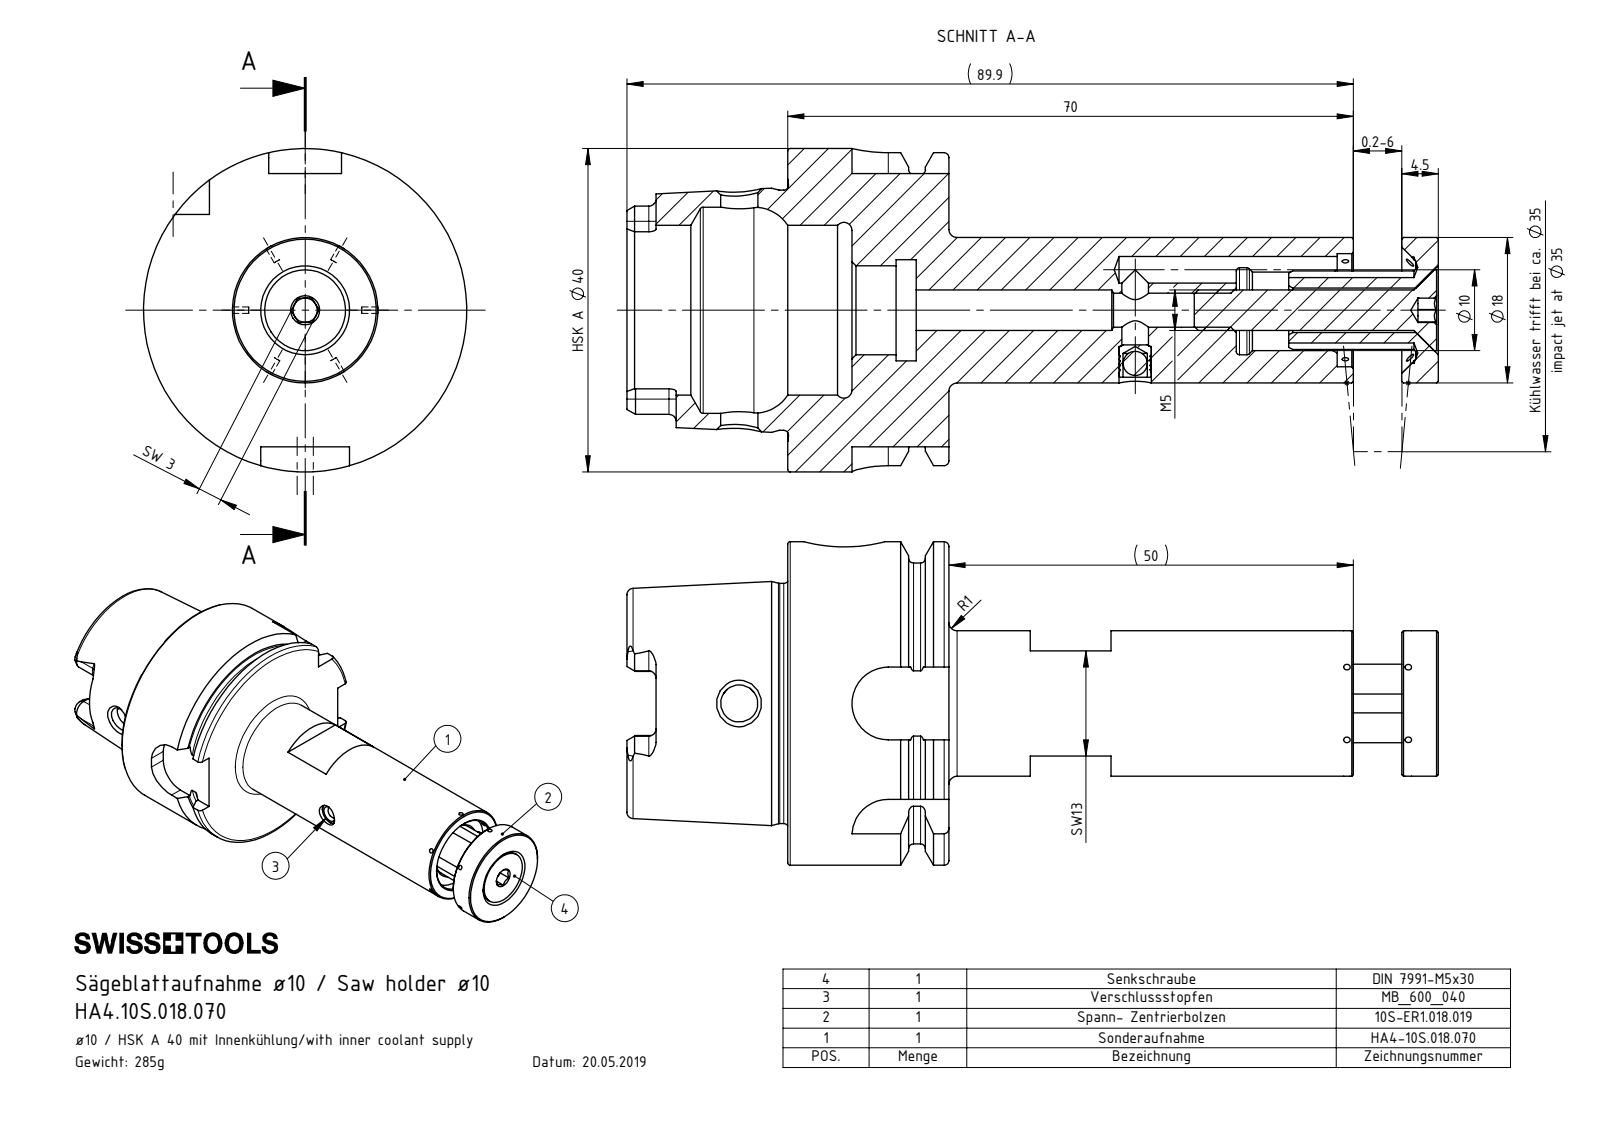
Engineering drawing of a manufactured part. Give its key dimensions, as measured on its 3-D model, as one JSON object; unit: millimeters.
{"part_name": "10S-ER1.018.019_A; HA4-10S.018.070_A_Fertigbearbeitung; KVT_MB_600_040; DIN 7991 - M5x30 (+2 more)", "step_written_by": "SolidWorks 2017 (AUTOMOTIVE_DESIGN)", "units": "millimeters", "bodies": {"solids": 5, "faces": 335, "planar": 72, "cylindrical": 114, "other": 149}, "overall_size": [100.4, 40, 40], "volume_mm3": 36326, "surface_area_mm2": 16059, "round_holes": [[0.8, 12], [3.3, 2], [3, 1], [4.2, 1], [4.6, 1], [5, 1], [5.5, 1], [10, 1], [11, 1], [12.5, 1], [14, 1], [21, 1]], "round_bosses_or_shafts": [[40, 1], [34.75, 1], [29.71, 1], [18, 1], [10, 1], [4, 1]], "partial_cylinders_radius": [[0.9, 6], [1.25, 4], [1.88, 4], [4.5, 4]], "face_to_face_distances": [19.95, 7.95, 12, 80.5, 72.55, 60.55, 19.9, 27.85, 39.85, 100.4], "hole_center_spacings": [9.25, 5, 49]}
